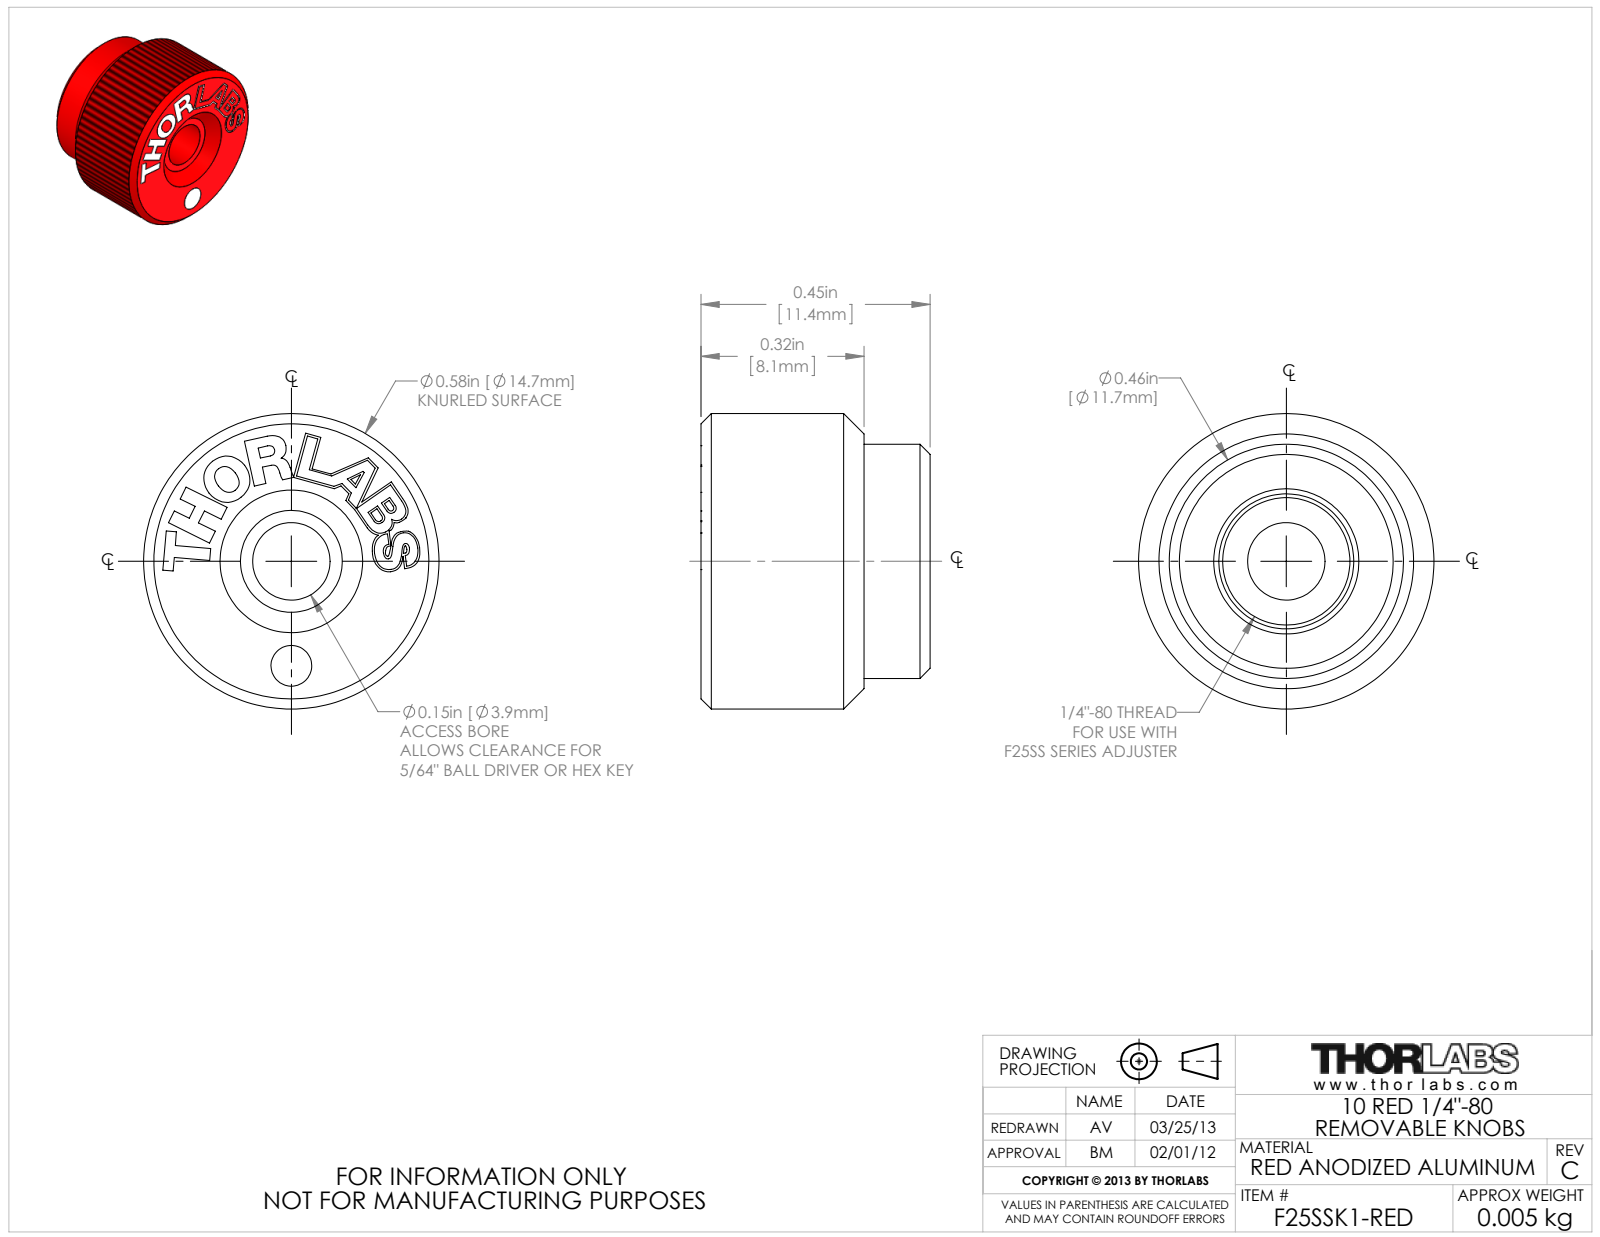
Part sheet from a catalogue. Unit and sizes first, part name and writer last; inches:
Units: inches
Overall size (bounding box): 0.58 × 0.58 × 0.45
Round holes (diameter × count): ⌀0.08 ×1, ⌀0.152 ×1, ⌀0.25 ×1, ⌀0.265 ×1, ⌀0.29 ×1
Round bosses / shafts (diameter × count): ⌀0.58 ×1, ⌀0.46 ×1
Partial cylindrical surfaces — rounded edges, fillets, slot ends (radius × count): R0.014 ×1, R0.047 ×1, R0.059 ×1
Main face-to-face distances: 0.45, 0.27, 0.18, 0.32, 0.05, 0.13, 0.02, 0.3, 0.03, 0.15
Hole centre spacings: 0.205
Volume: 0.088 in³ · Surface area: 1.477 in²
Bodies: 1 solid, 210 faces (118 planar, 21 cylindrical, 71 other)
Part name (STEP PRODUCT): 23387-E0W
STEP written by: SolidWorks 2012 (AUTOMOTIVE_DESIGN)
